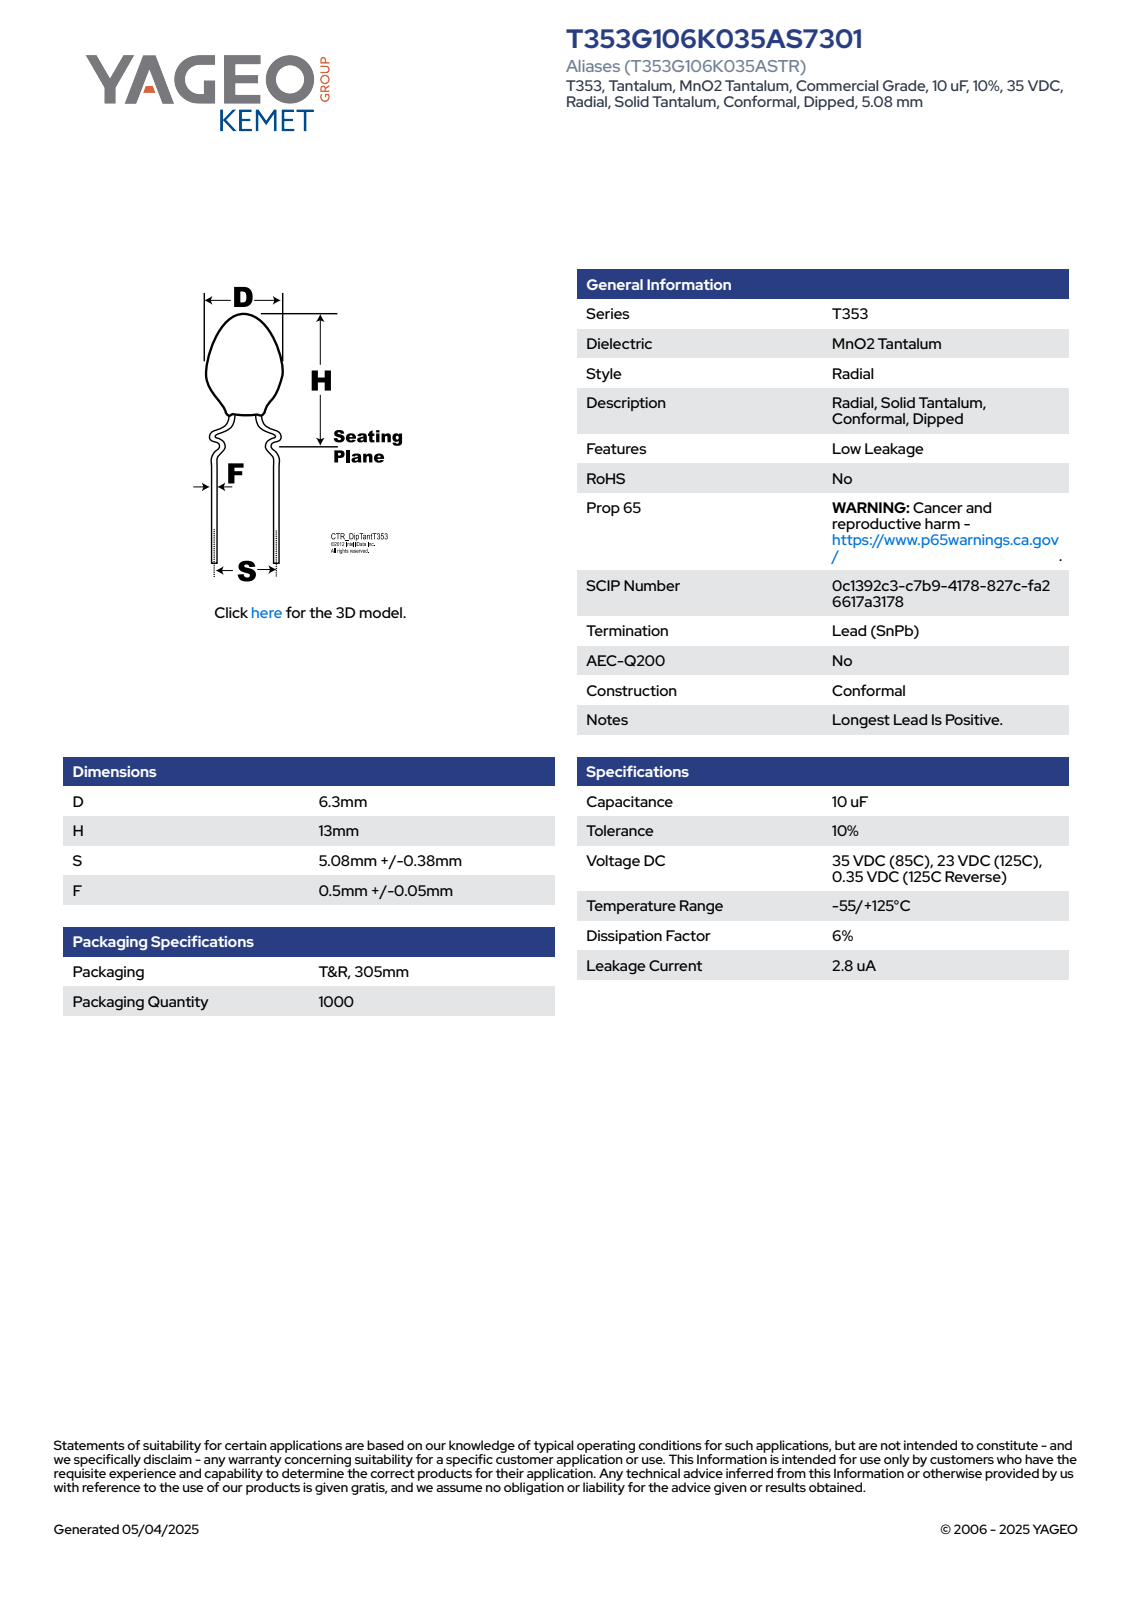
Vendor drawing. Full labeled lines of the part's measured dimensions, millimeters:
Part name (STEP PRODUCT): CTR_T353_D6.3H13S5.08LL5.56F0.55
STEP written by: SolidWorks 2014 (AUTOMOTIVE_DESIGN)
Units: millimetres
Bodies: 1 solid, 89 faces (29 planar, 10 cylindrical, 50 other)
Overall size (bounding box): 18.56 × 6.3 × 6.3
Volume: 243 mm³ · Surface area: 232 mm²
Round bosses / shafts (diameter × count): ⌀0.55 ×2, ⌀6.3 ×1
Partial cylindrical surfaces — rounded edges, fillets, slot ends (radius × count): R3.14 ×1
Main face-to-face distances: 8.92, 9.64, 18.56, 4.21, 4.71, 14.66, 5.02, 3.9, 13.85, 0.81
